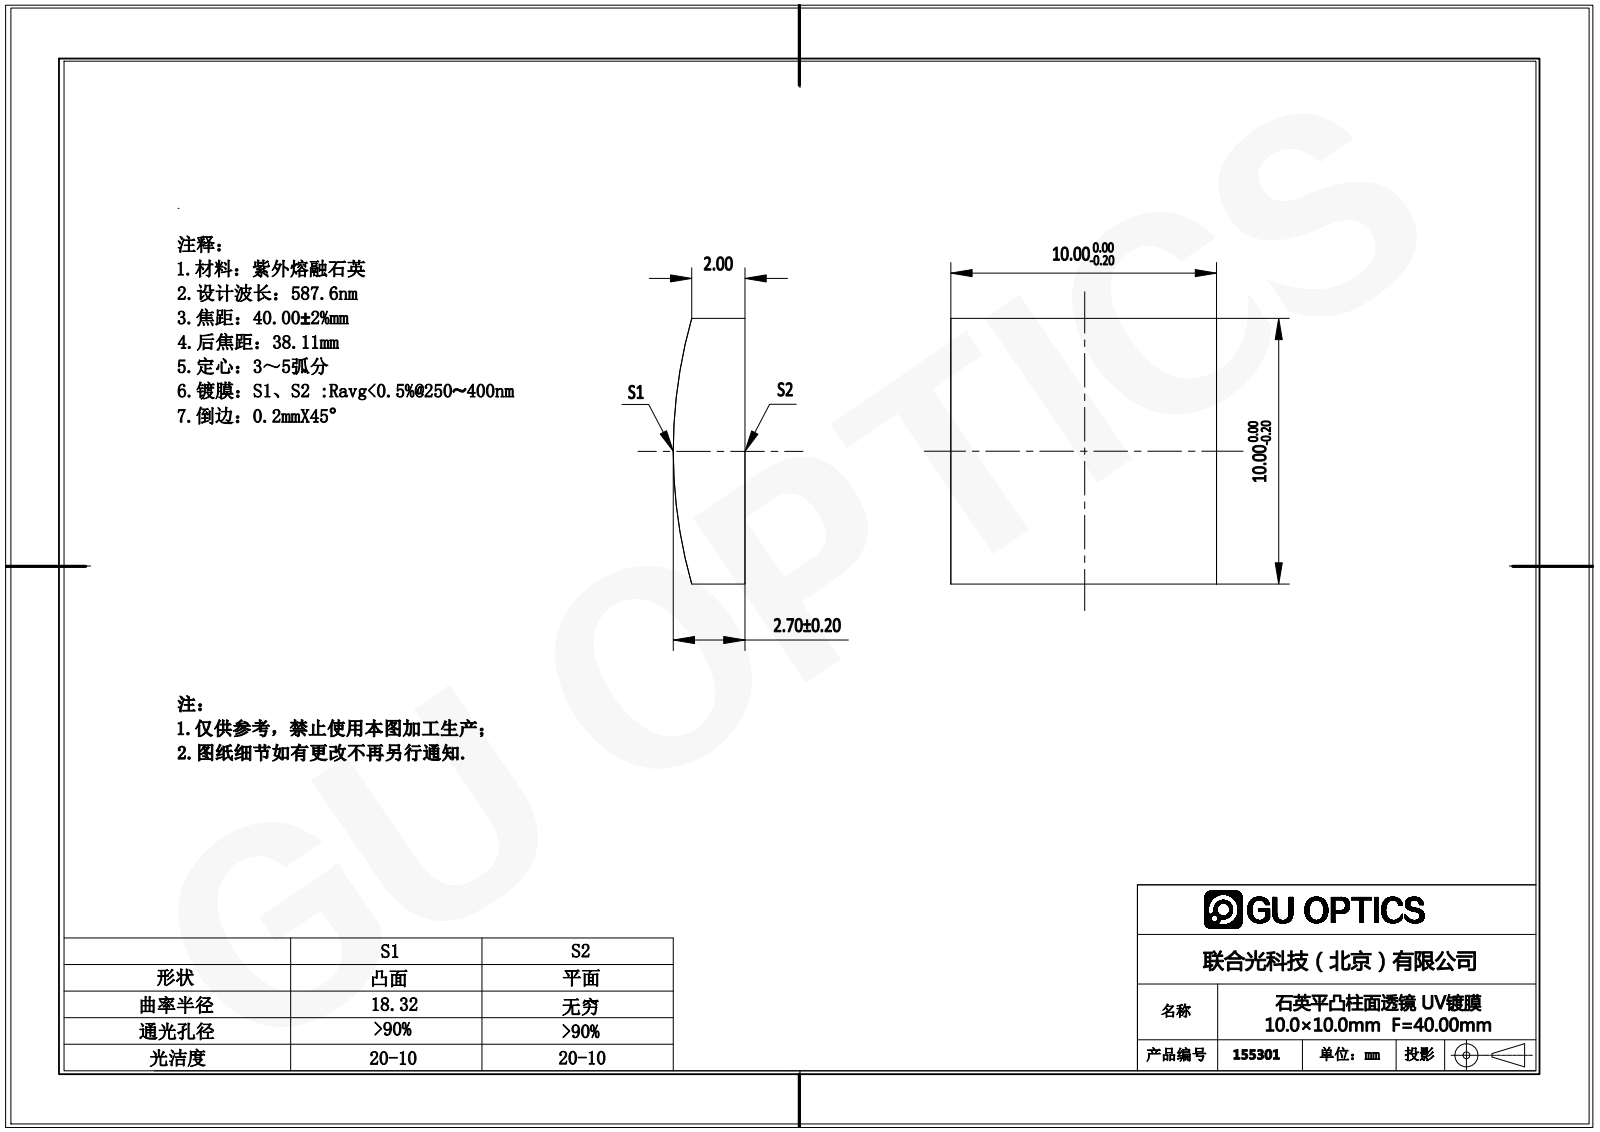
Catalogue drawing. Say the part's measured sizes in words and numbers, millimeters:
The part is named "155267". Its 3-D file was written by "SolidWorks 2016 (AUTOMOTIVE_DESIGN)". It is 1 solid with 6 faces: 5 planar, 1 cylindrical and 0 other. Overall it measures 10 by 10 by 2.7 millimeters. Its volume is 247 cubic millimeters and its surface area 291 square millimeters. Partial cylindrical surfaces (rounded edges, fillets, slot ends): 1 of radius 18.32. The main face-to-face distances are 10.
